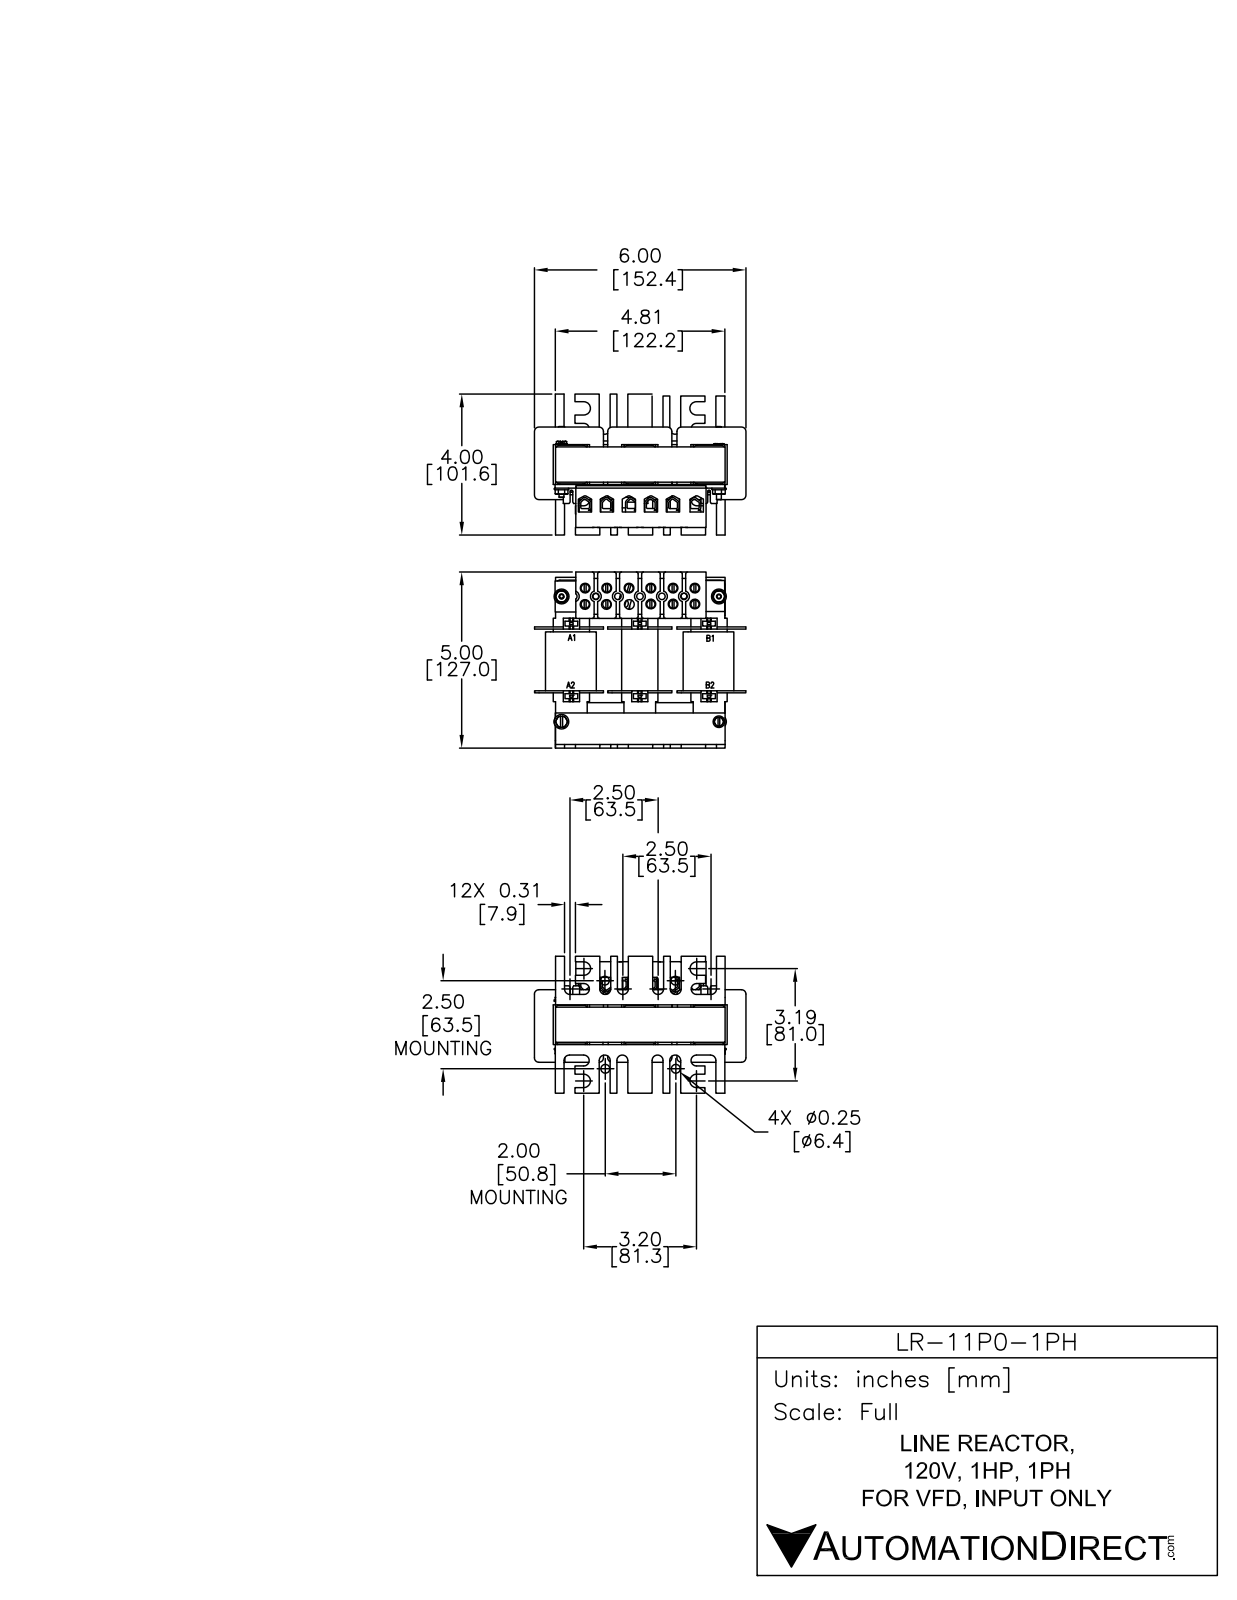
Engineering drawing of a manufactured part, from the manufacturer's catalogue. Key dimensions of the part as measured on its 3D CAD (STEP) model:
Part name (STEP PRODUCT): LR-11P0-1PH
STEP written by: SolidWorks 2011 (AUTOMOTIVE_DESIGN)
Units: millimetres
Bodies: 43 solids, 1048 faces (794 planar, 222 cylindrical, 32 other)
Overall size (bounding box): 144.75 × 131.2 × 98.38
Volume: 540 879 mm³ · Surface area: 167 068 mm²
Round holes (diameter × count): ⌀7 ×12, ⌀7.75 ×5
Round bosses / shafts (diameter × count): ⌀7 ×12, ⌀10.25 ×4, ⌀8 ×4, ⌀7.75 ×2, ⌀7.5 ×2, ⌀3.4 ×2, ⌀3.25 ×2
Partial cylindrical surfaces — rounded edges, fillets, slot ends (radius × count): R3.94 ×16, R1.82 ×12, R2.68 ×12, R2.71 ×12, R5 ×12, R6 ×12, R4.83 ×4, R0.86 ×3
Main face-to-face distances: 2.5, 27.26, 1.5, 31.25, 5.62, 34.88, 28.76, 34.38, 7.12, 32.88
Hole centre spacings: 16, 32, 21.26, 34.93, 48, 14, 50, 10.34
